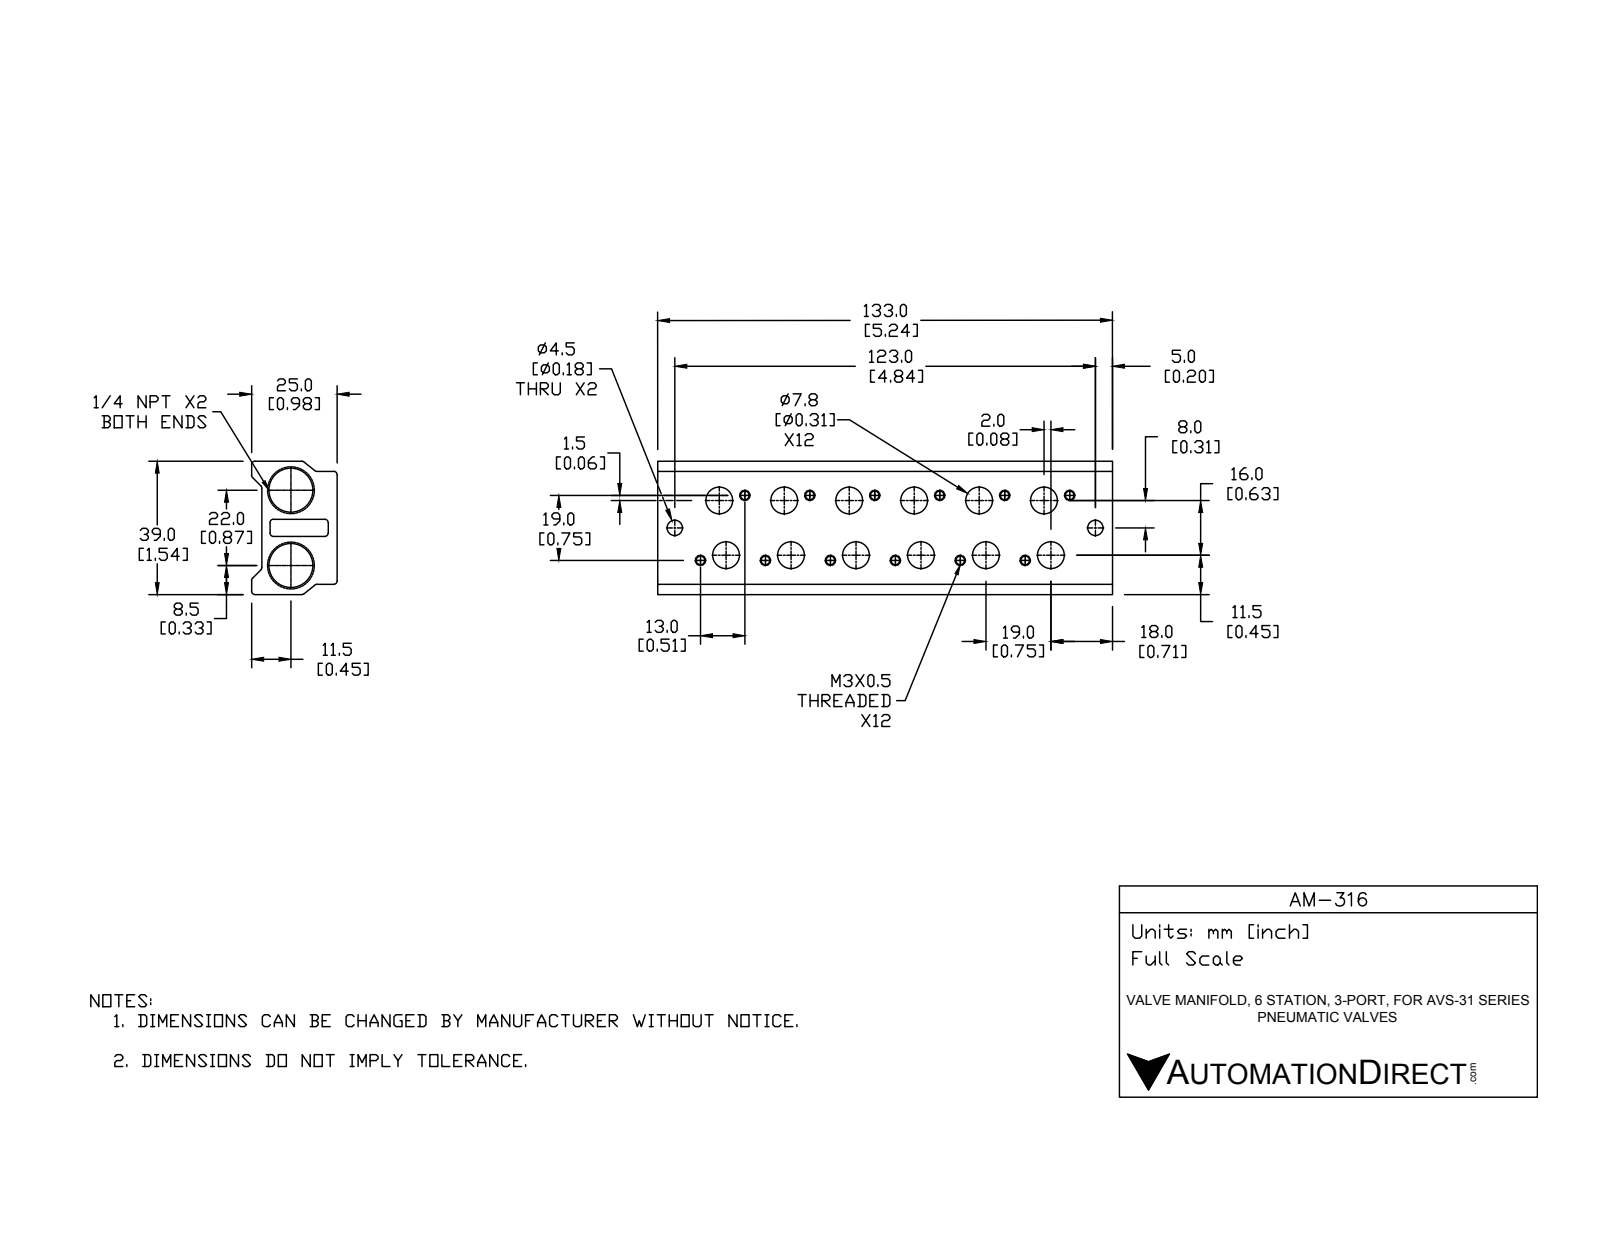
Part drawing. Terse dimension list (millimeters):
name: AM-316
written by: SolidWorks 2018 (AUTOMOTIVE_DESIGN)
unit: mm
bodies: 1 solid, 182 faces (26 planar, 94 cylindrical, 62 other)
size: 133 × 39 × 25
volume: 67 573 mm³; area: 35 172 mm²
holes: 12× ⌀2.5, 12× ⌀7.8, 2× ⌀4.5, 2× ⌀11.11, 2× ⌀11.13
rounds: 16× R1
face distances: 22, 17, 3, 5, 39, 36, 14, 19, 25, 33
hole spacings: 19, 38, 7.65, 18.34, 57, 11.6, 22.1, 26.54
